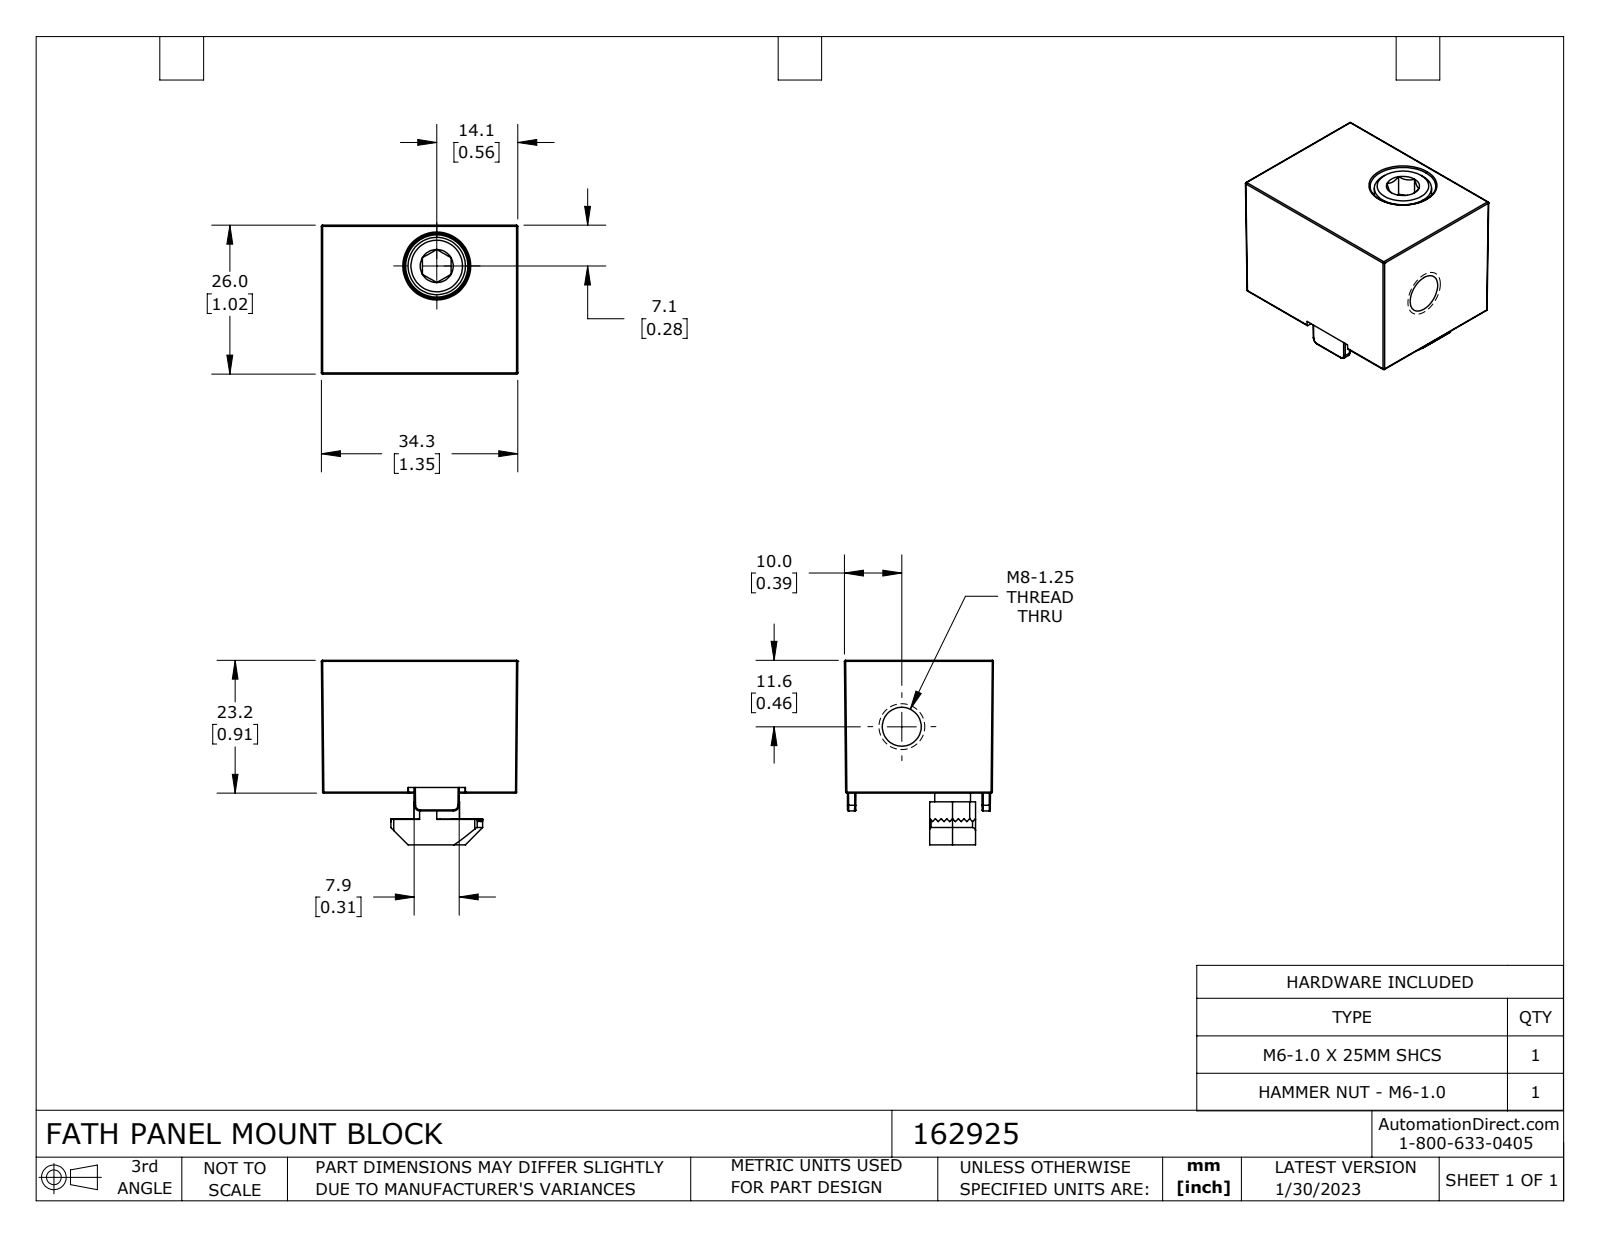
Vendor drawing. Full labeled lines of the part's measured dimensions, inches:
Part name (STEP PRODUCT): 162925
STEP written by: SolidWorks 2021 (CONFIG_CONTROL_DESIGN)
Units: inches
Bodies: 2 solids, 300 faces (100 planar, 102 cylindrical, 98 other)
Overall size (bounding box): 1.349 × 1.268 × 1.023
Volume: 0.905 in³ · Surface area: 13.62 in²
Round holes (diameter × count): ⌀0.197 ×1, ⌀0.268 ×1
Round bosses / shafts (diameter × count): ⌀0.394 ×1, ⌀0.246 ×1
Partial cylindrical surfaces — rounded edges, fillets, slot ends (radius × count): R0.008 ×34, R0.02 ×19, R0.004 ×7, R0.039 ×4, R0.157 ×1, R0.213 ×1, R0.315 ×1
Main face-to-face distances: 0.913, 0.908, 0.672, 0.315, 0.594, 0.319, 0.118, 0.369, 0.354, 0.937
